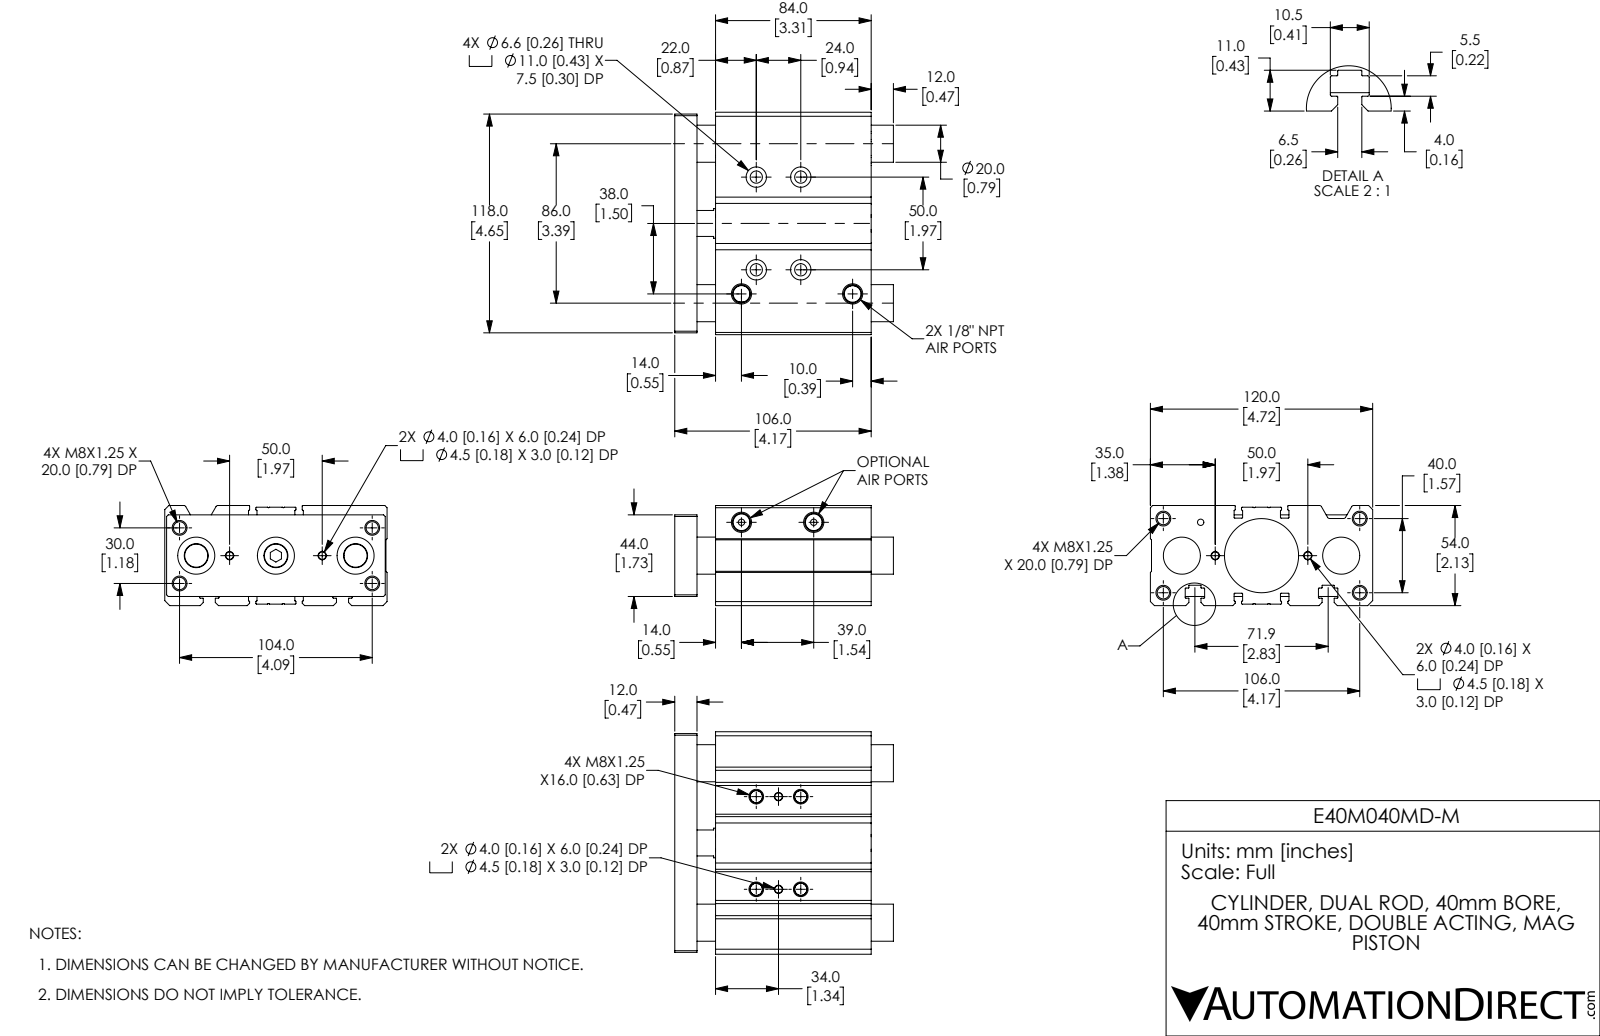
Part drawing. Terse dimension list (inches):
name: E40M040MD-M; E40M040MD-M_ENDPLATE; E40M040MD-M_BODY
written by: SolidWorks 2019 (CONFIG_CONTROL_DESIGN)
unit: in
bodies: 5 solids, 427 faces (139 planar, 194 cylindrical, 94 other)
size: 4.724 × 4.646 × 2.126
volume: 31.69 in³; area: 189.4 in²
holes: 12× ⌀0.262, 4× ⌀0.157, 4× ⌀0.177, 4× ⌀0.26, 4× ⌀0.433, 3× ⌀0.394, 3× ⌀0.787, 2× ⌀0.135, 2× ⌀0.43, 2× ⌀0.51, 1× ⌀0.135, 1× ⌀0.787
bosses: 1× ⌀0.63, 1× ⌀0.51
rounds: 32× R0.008, 28× R0.016, 4× R0.047, 2× R0.012
face distances: 2.126, 0.472, 4.173, 0.866, 0.394, 3.701, 3.307, 3.504, 0.163, 1.896
hole spacings: 0.201, 0.472, 0.689, 0.88, 1.216, 1.355, 1.378, 1.969
